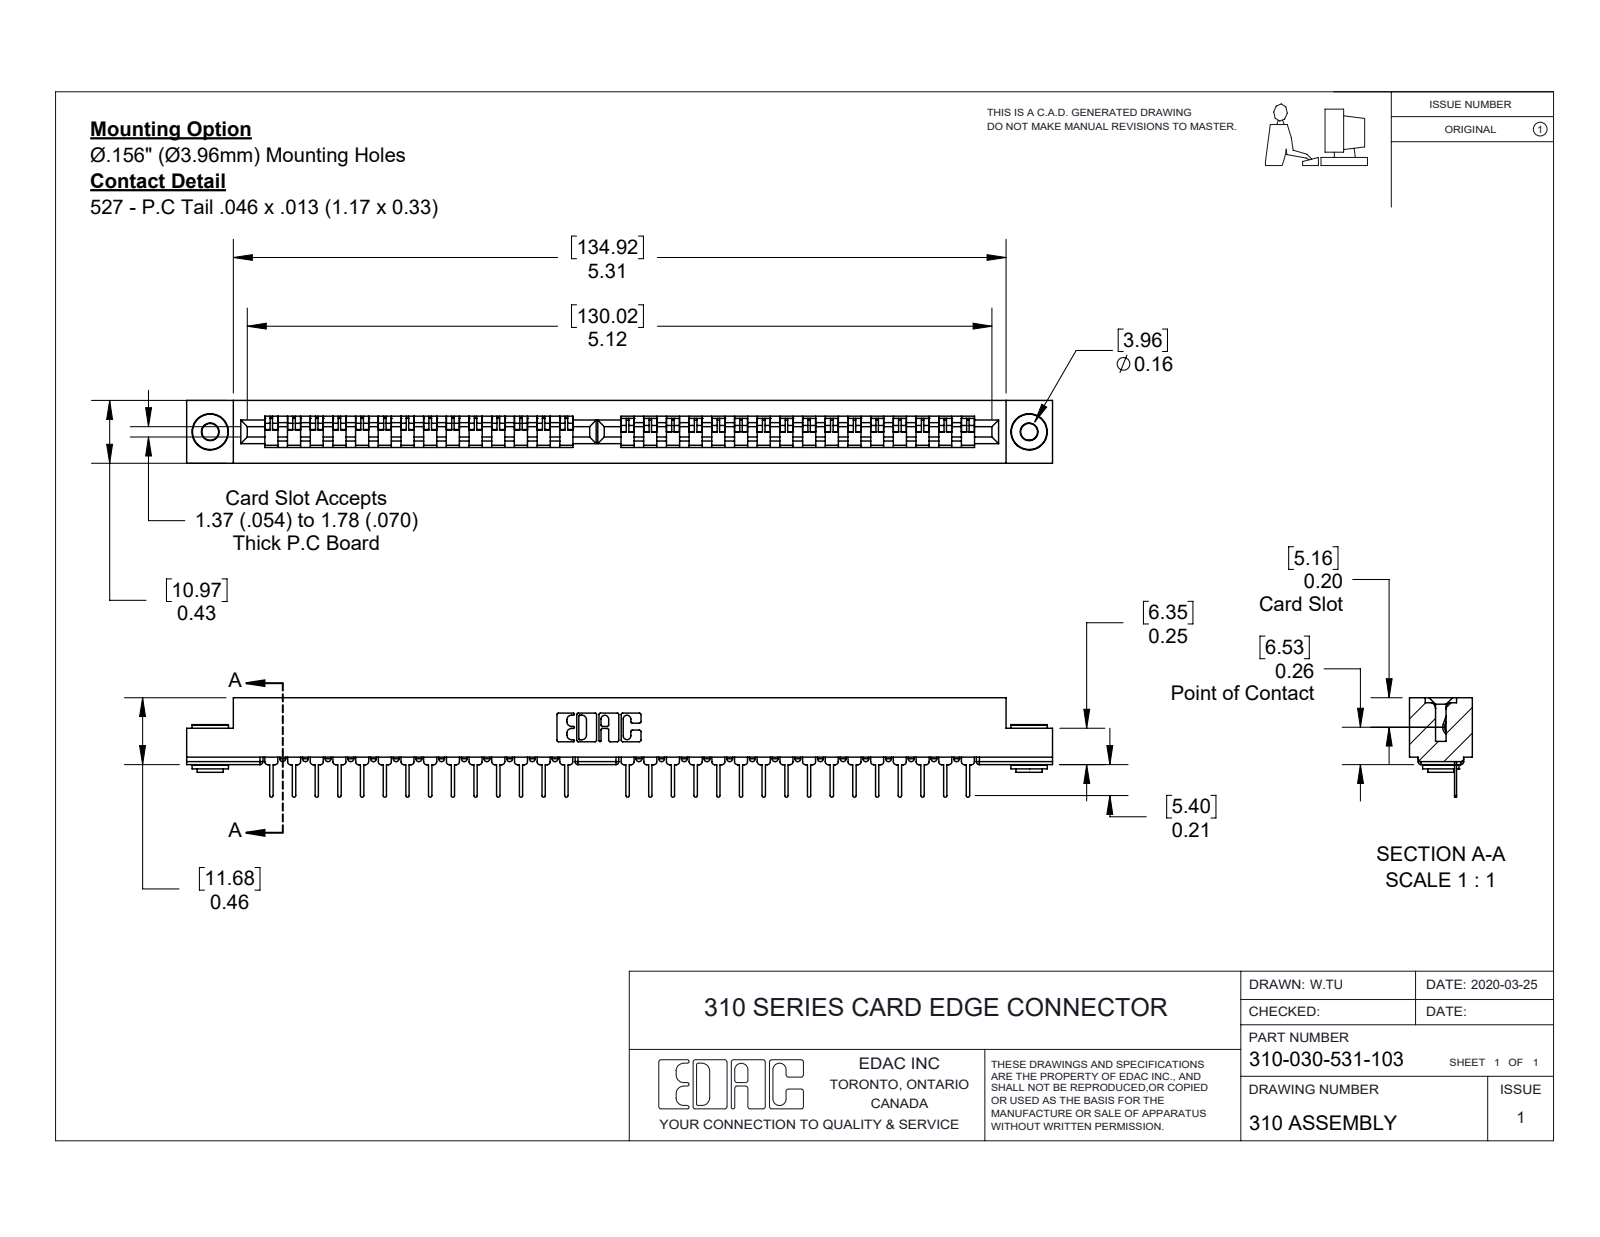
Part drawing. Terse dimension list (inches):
name: 307-290-001_531; 310 Part_.116 Hex; 310-030-531-103; 345-250-002_345-250-002-102
written by: SolidWorks 2016 (CONFIG_CONTROL_DESIGN)
unit: in
bodies: 33 solids, 1898 faces (1218 planar, 608 cylindrical, 72 other)
size: 5.953 × 0.684 × 0.432
volume: 0.77 in³; area: 23.1 in²
holes: 2× ⌀0.116, 2× ⌀0.156
bosses: 2× ⌀0.25, 2× ⌀0.18, 2× ⌀0.136
rounds: 158× R0.02, 30× R0.011, 22× R0.01, 6× R0.007, 6× R0.031, 3× R0.026, 2× R0.012, 2× R0.025
face distances: 0.109, 0.324, 0.432, 0.072, 0.015, 0.013, 0.409, 0.215, 0.252, 0.18
hole spacings: 5.63
